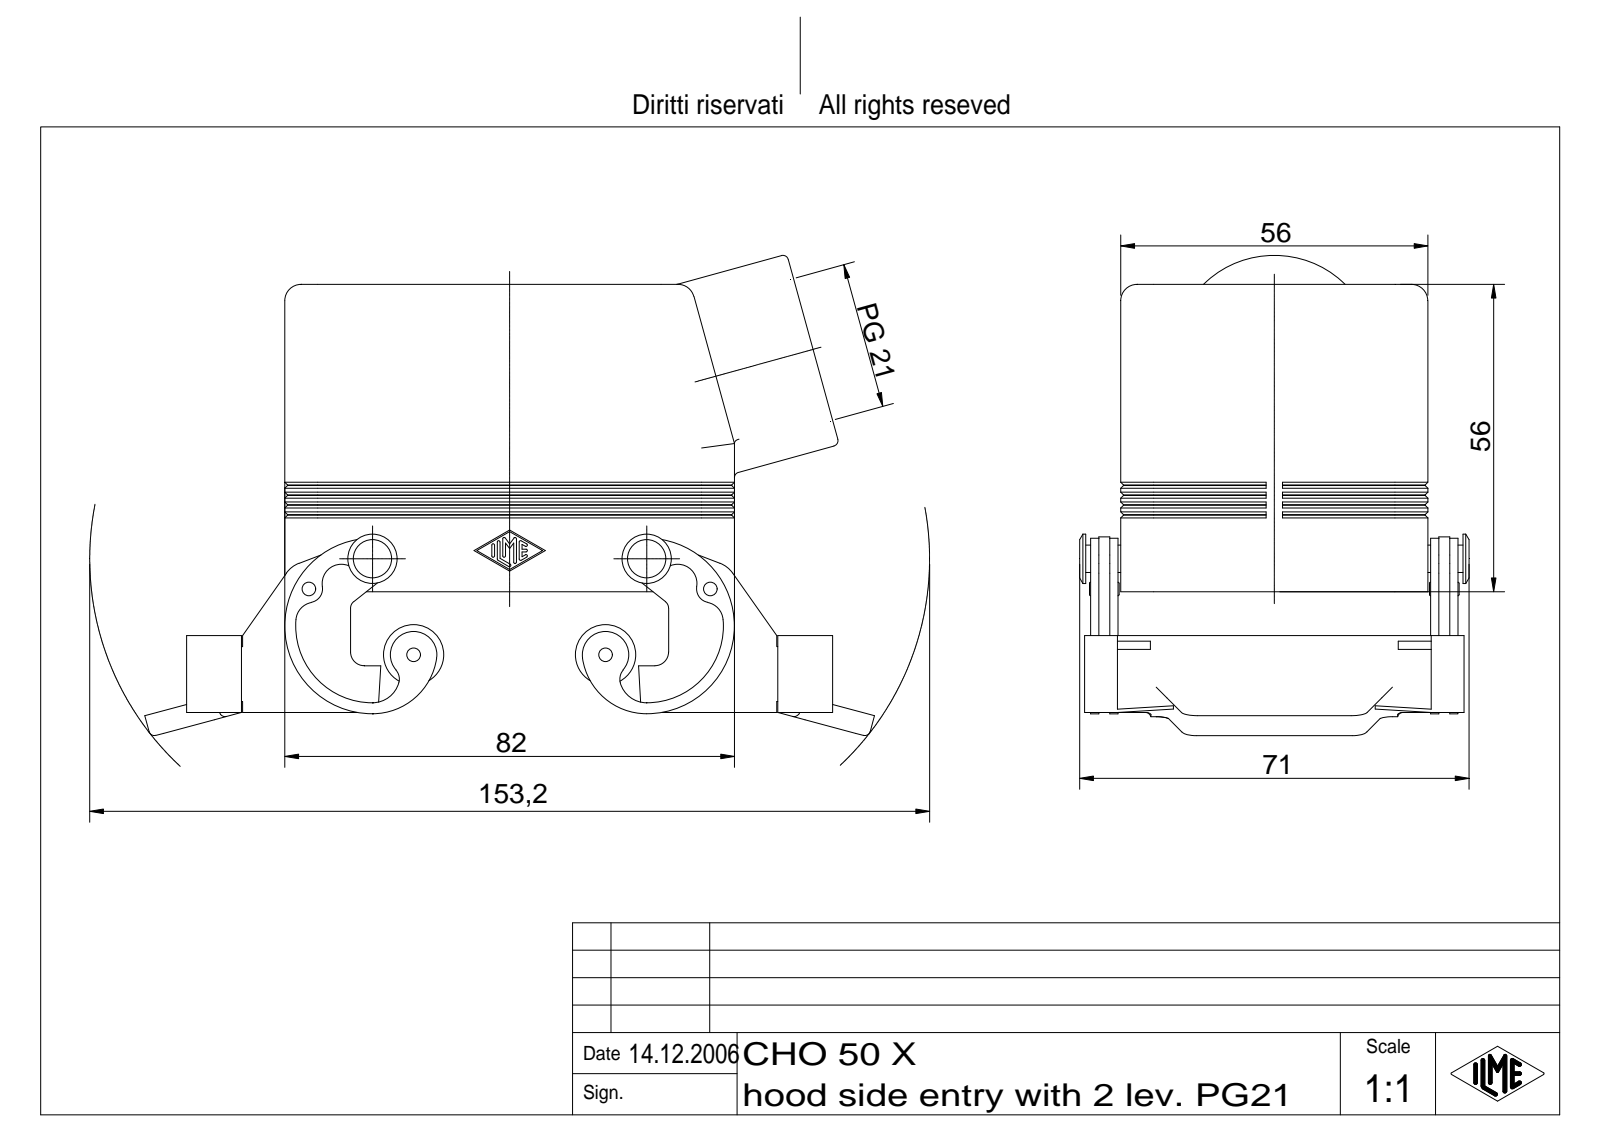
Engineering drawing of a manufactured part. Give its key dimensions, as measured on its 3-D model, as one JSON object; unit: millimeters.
{"part_name": "CHO 50 X", "step_written_by": "Autodesk Inventor 7 (AUTOMOTIVE_DESIGN)", "units": "millimeters", "bodies": {"solids": 1, "faces": 880, "planar": 242, "cylindrical": 252, "other": 386}, "overall_size": [133.07, 87.5, 71], "volume_mm3": 98502, "surface_area_mm2": 59428, "round_holes": [[2.46, 4], [3.5, 4], [2.5, 2], [24.78, 1], [26.78, 1]], "round_bosses_or_shafts": [[11, 2], [9, 2], [5, 2], [2, 2], [36, 1]], "partial_cylinders_radius": [[0.25, 14], [2, 14], [3, 12], [1, 8], [2.5, 6], [6, 6], [3.5, 4], [5, 4]], "face_to_face_distances": [3, 53, 56, 50, 2, 79, 4, 60, 62, 5], "hole_center_spacings": [16, 66, 67.91, 73.2]}
